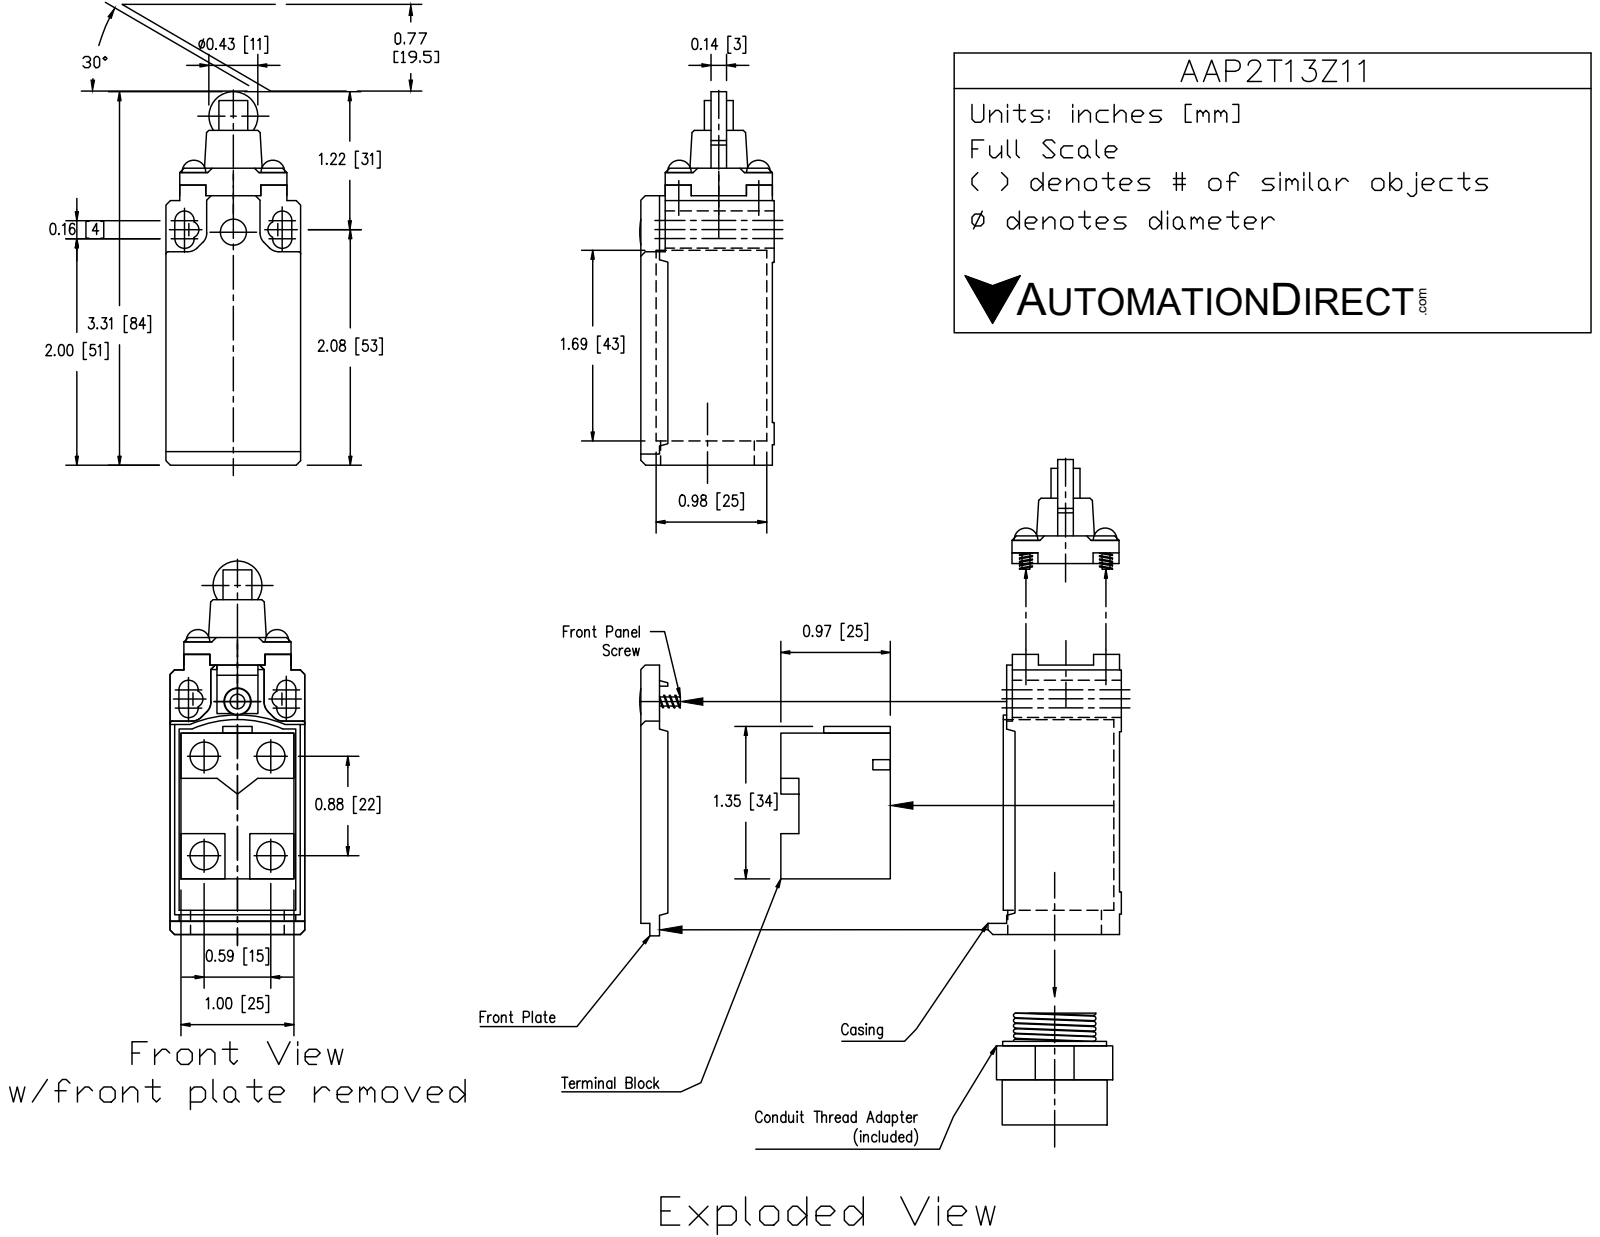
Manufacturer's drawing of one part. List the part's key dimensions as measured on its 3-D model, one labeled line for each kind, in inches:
Part name (STEP PRODUCT): AAP2T13Z11
STEP written by: SolidWorks 2017 (AUTOMOTIVE_DESIGN)
Units: inches
Bodies: 4 solids, 202 faces (115 planar, 60 cylindrical, 27 other)
Overall size (bounding box): 3.291 × 1.205 × 1.193
Volume: 3.371 in³ · Surface area: 21.29 in²
Round holes (diameter × count): ⌀0.236 ×1, ⌀0.319 ×1, ⌀0.669 ×1, ⌀0.748 ×1
Round bosses / shafts (diameter × count): ⌀0.22 ×6, ⌀0.425 ×1, ⌀0.315 ×1
Partial cylindrical surfaces — rounded edges, fillets, slot ends (radius × count): R0.039 ×8, R0.118 ×8, R0.079 ×6, R0.394 ×1, R0.4 ×1, R0.787 ×1
Main face-to-face distances: 1.193, 1.165, 0.016, 2.406, 1.181, 0.236, 0.945, 0.15, 0.124, 1.069
Hole centre spacings: 0.083
